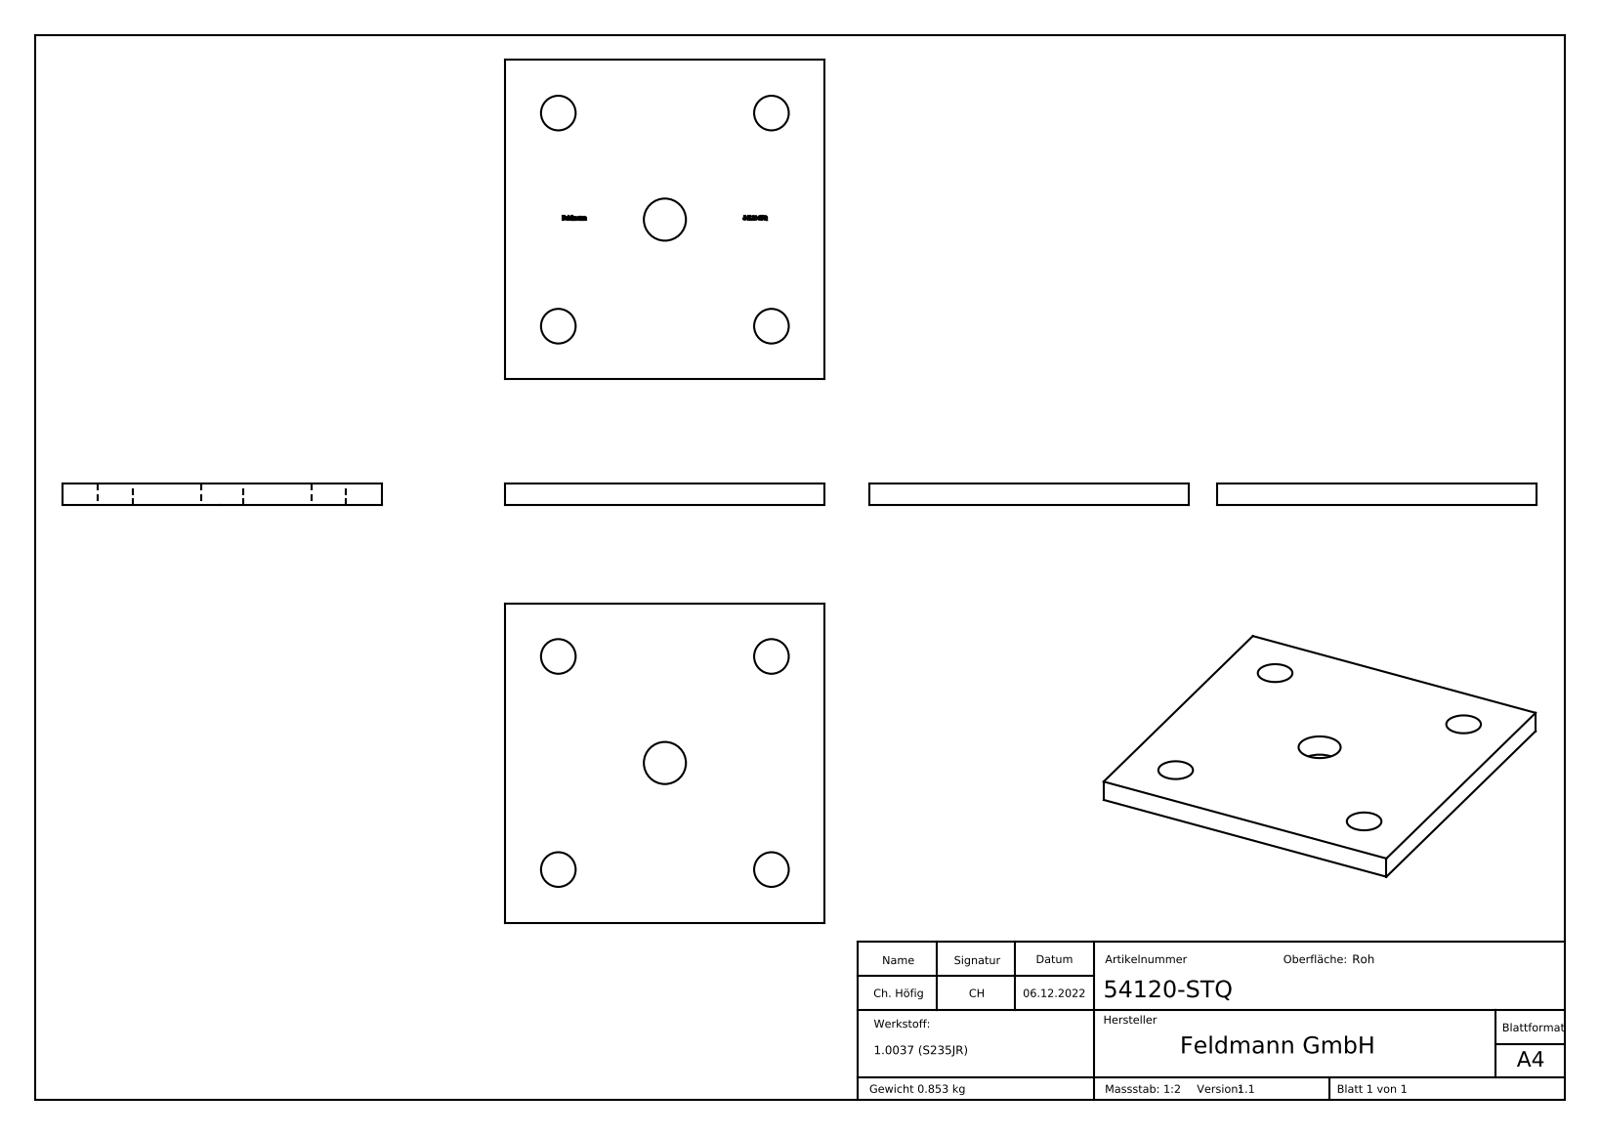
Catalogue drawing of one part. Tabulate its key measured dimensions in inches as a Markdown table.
| quantity | value |
| --- | --- |
| part name | 54120-STQ |
| STEP written by | SolidWorks 2018 (CONFIG_CONTROL_DESIGN) |
| units | inches |
| bodies | 1 solid, 235 faces (134 planar, 5 cylindrical, 96 other) |
| overall size | 4.724 × 4.724 × 0.315 |
| volume | 6.675 in³ |
| surface area | 51 in² |
| round holes (diameter × count) | 0.512 × 4, 0.622 × 1 |
| main face-to-face distances | 0.315, 4.724, 0.311, 2.362, 0.052, 2.684, 2.938, 2.414, 2.31, 0.206 |
| hole center spacings | 2.227, 3.15, 4.454 |
